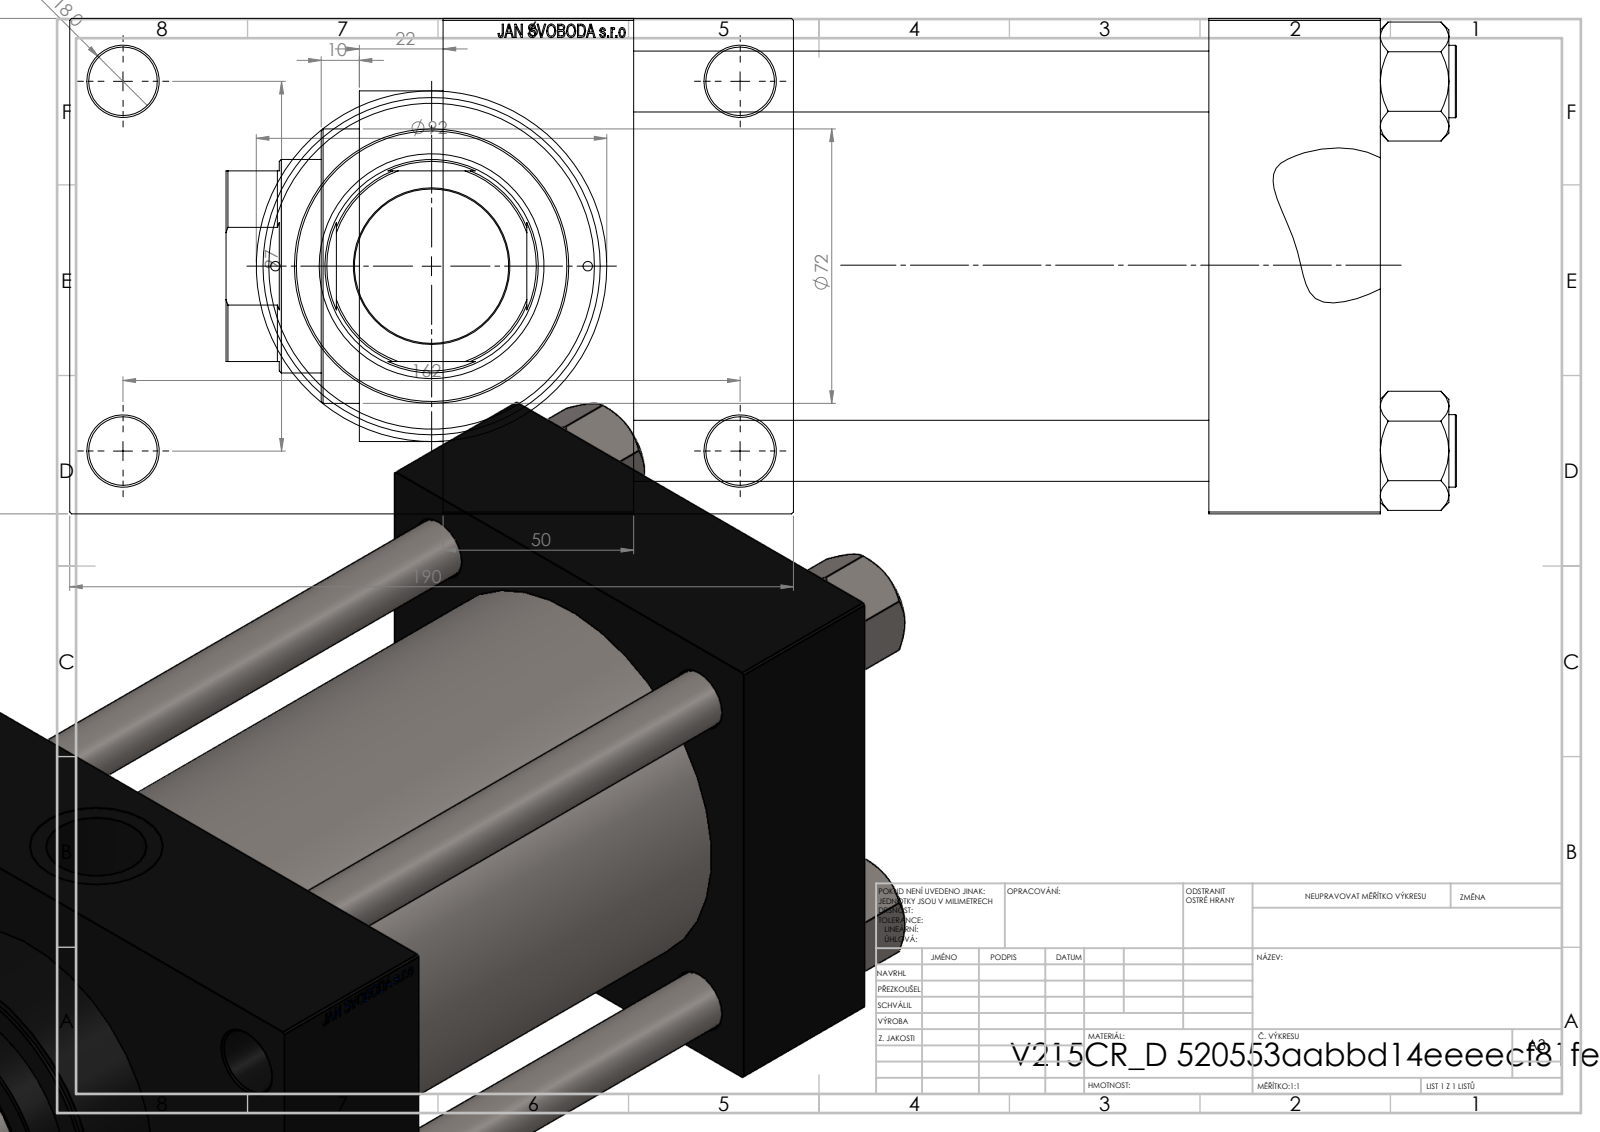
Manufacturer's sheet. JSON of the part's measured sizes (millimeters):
{"part_name": "V215CR_VCP_D; V215CR_D_TYCINKA; NUT_M5_D; V215_VC_A (+1 more)", "step_written_by": "SolidWorks 2019 (CONFIG_CONTROL_DESIGN)", "units": "millimeters", "bodies": {"solids": 11, "faces": 1160, "planar": 547, "cylindrical": 93, "other": 520}, "overall_size": [323, 190, 130], "volume_mm3": 2983000, "surface_area_mm2": 441652, "round_holes": [[16, 4], [18, 4], [2.5, 2], [7, 2], [26.44, 2], [35, 2], [40.5, 1], [56, 1], [59, 1], [76, 1], [85.5, 1], [100, 1]], "round_bosses_or_shafts": [[19, 4], [106, 1], [92, 1], [72, 1]], "partial_cylinders_radius": [[27, 1]], "face_to_face_distances": [130, 50, 45, 196, 151, 246, 201, 30, 160, 190], "hole_center_spacings": [32.55, 49.02, 62.87, 68.52, 94.41, 96.9, 101.73, 102.27]}
